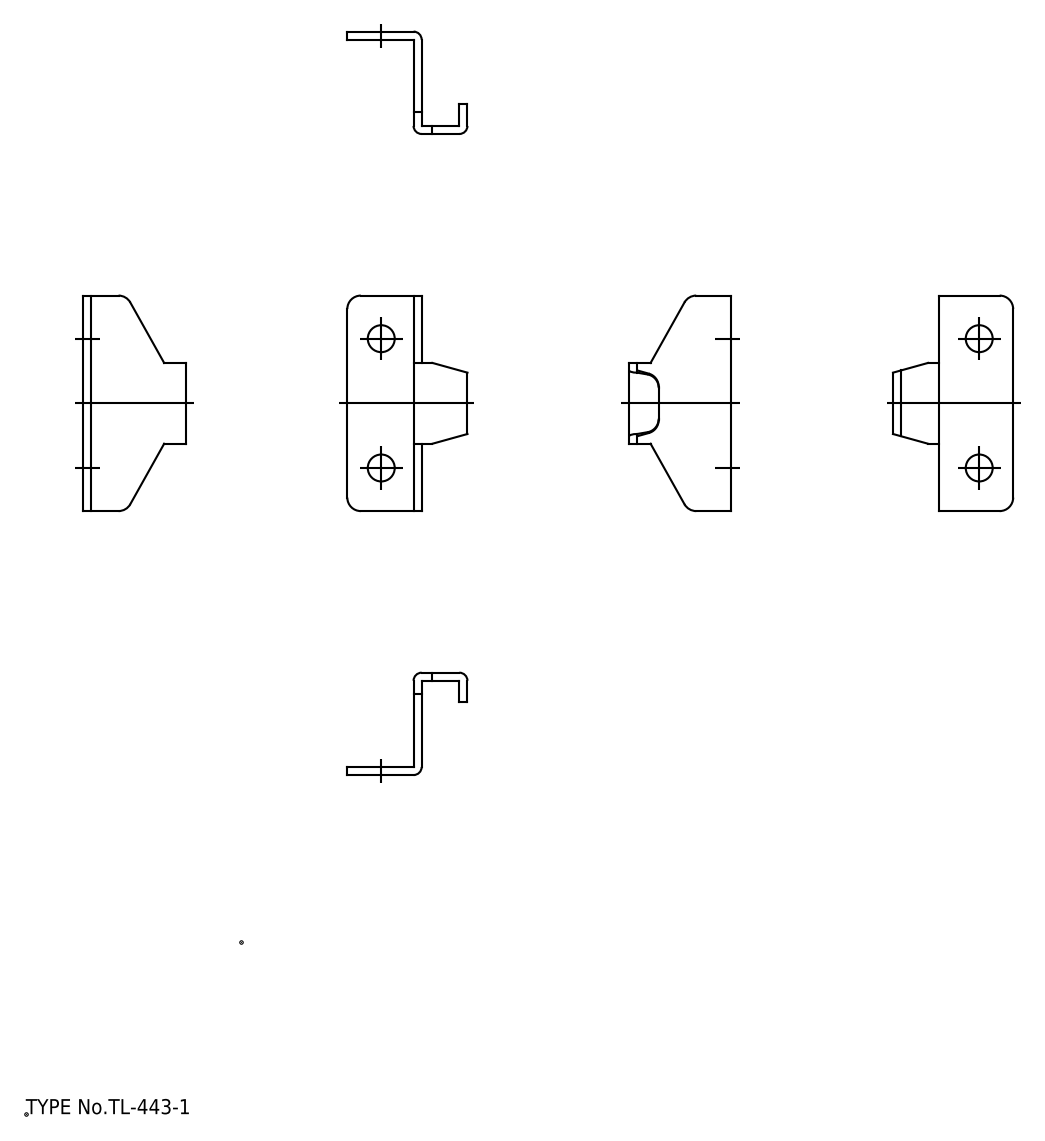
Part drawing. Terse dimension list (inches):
written by: spGate 19.8.4 (****-****-****-****) (AUTOMOTIVE_DESIGN)
unit: in
bodies: 1 solid, 33 faces (18 planar, 11 cylindrical, 4 other)
size: 1.575 × 0.878 × 0.748
volume: 0.106 in³; area: 4.005 in²
holes: 2× ⌀0.197
rounds: 4× R0.098, 3× R0.059
face distances: 0.059, 0.689, 0.748, 0.63, 0.335, 0.484, 0.543, 0.819, 0.276, 0.878
hole spacings: 0.945
